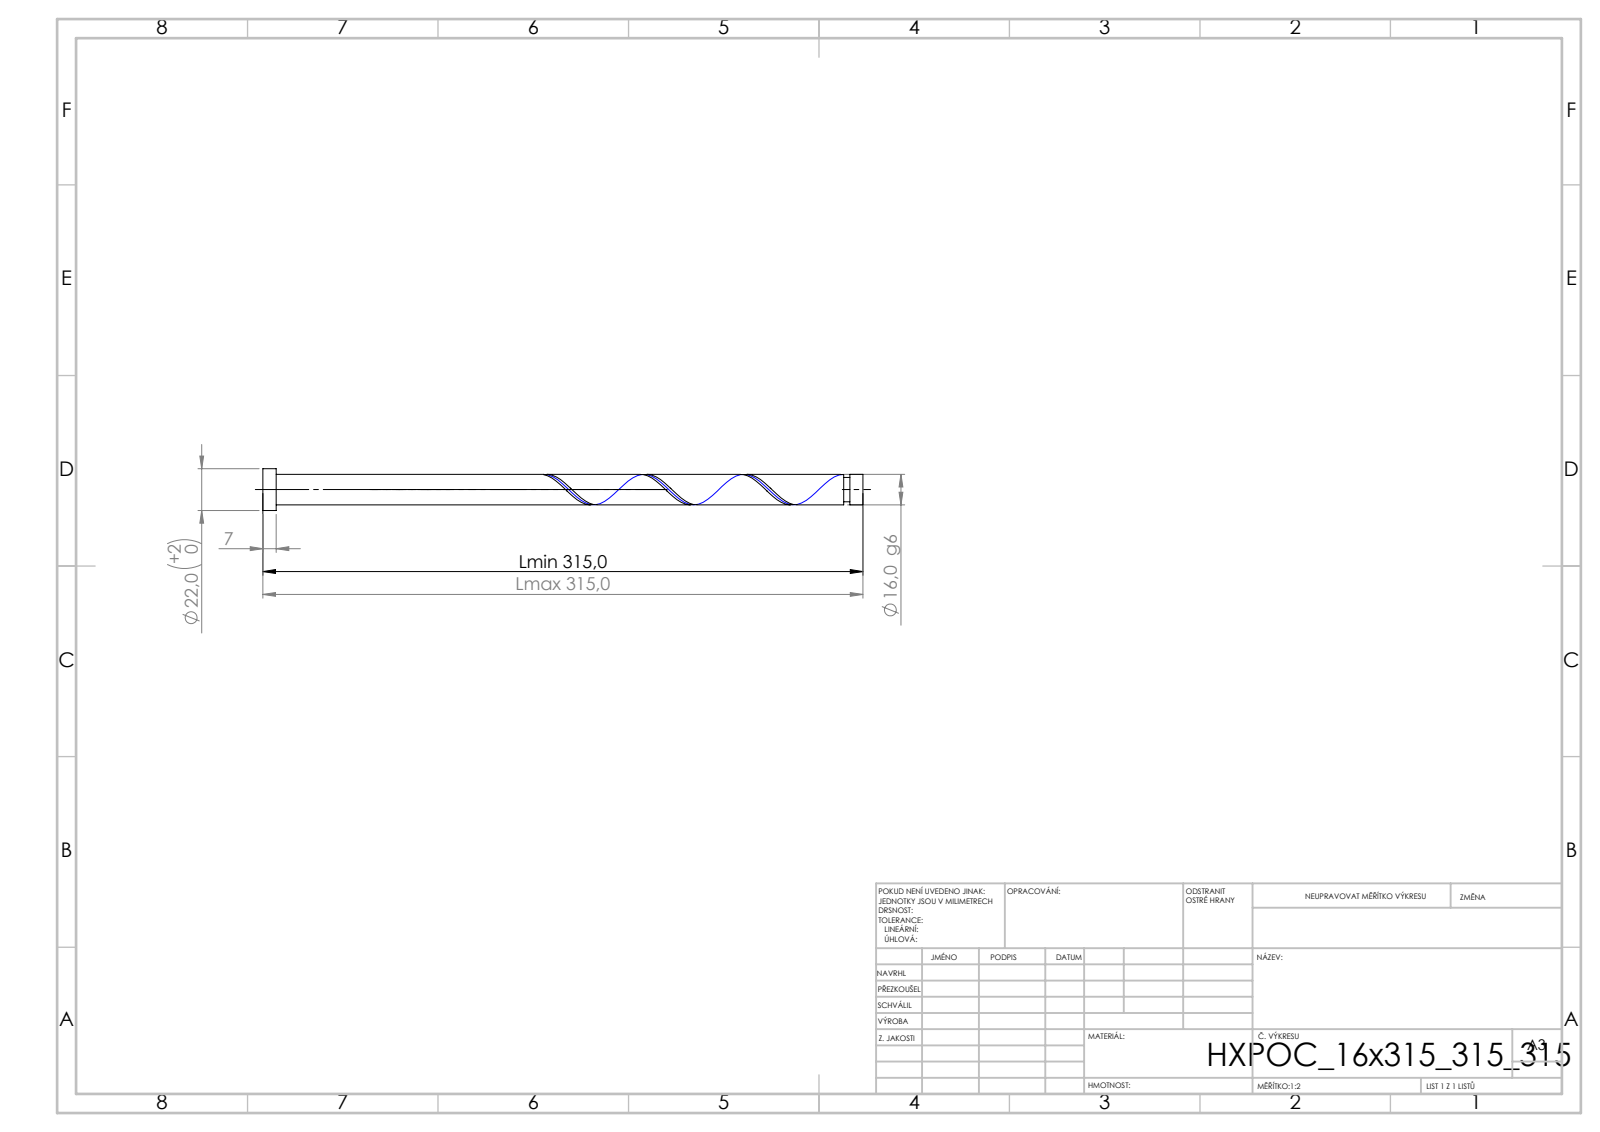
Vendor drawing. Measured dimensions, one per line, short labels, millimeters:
written by: SolidWorks 2019 (CONFIG_CONTROL_DESIGN)
unit: mm
bodies: 1 solid, 21 faces (6 planar, 14 cylindrical, 1 other)
size: 315 × 22 × 22
volume: 63 750 mm³; area: 17 214 mm²
bosses: 1× ⌀22, 1× ⌀16, 1× ⌀12.8
face distances: 315, 7, 308, 308.16, 301.16, 6.84, 304.96, 297.96, 3.2, 10.04
